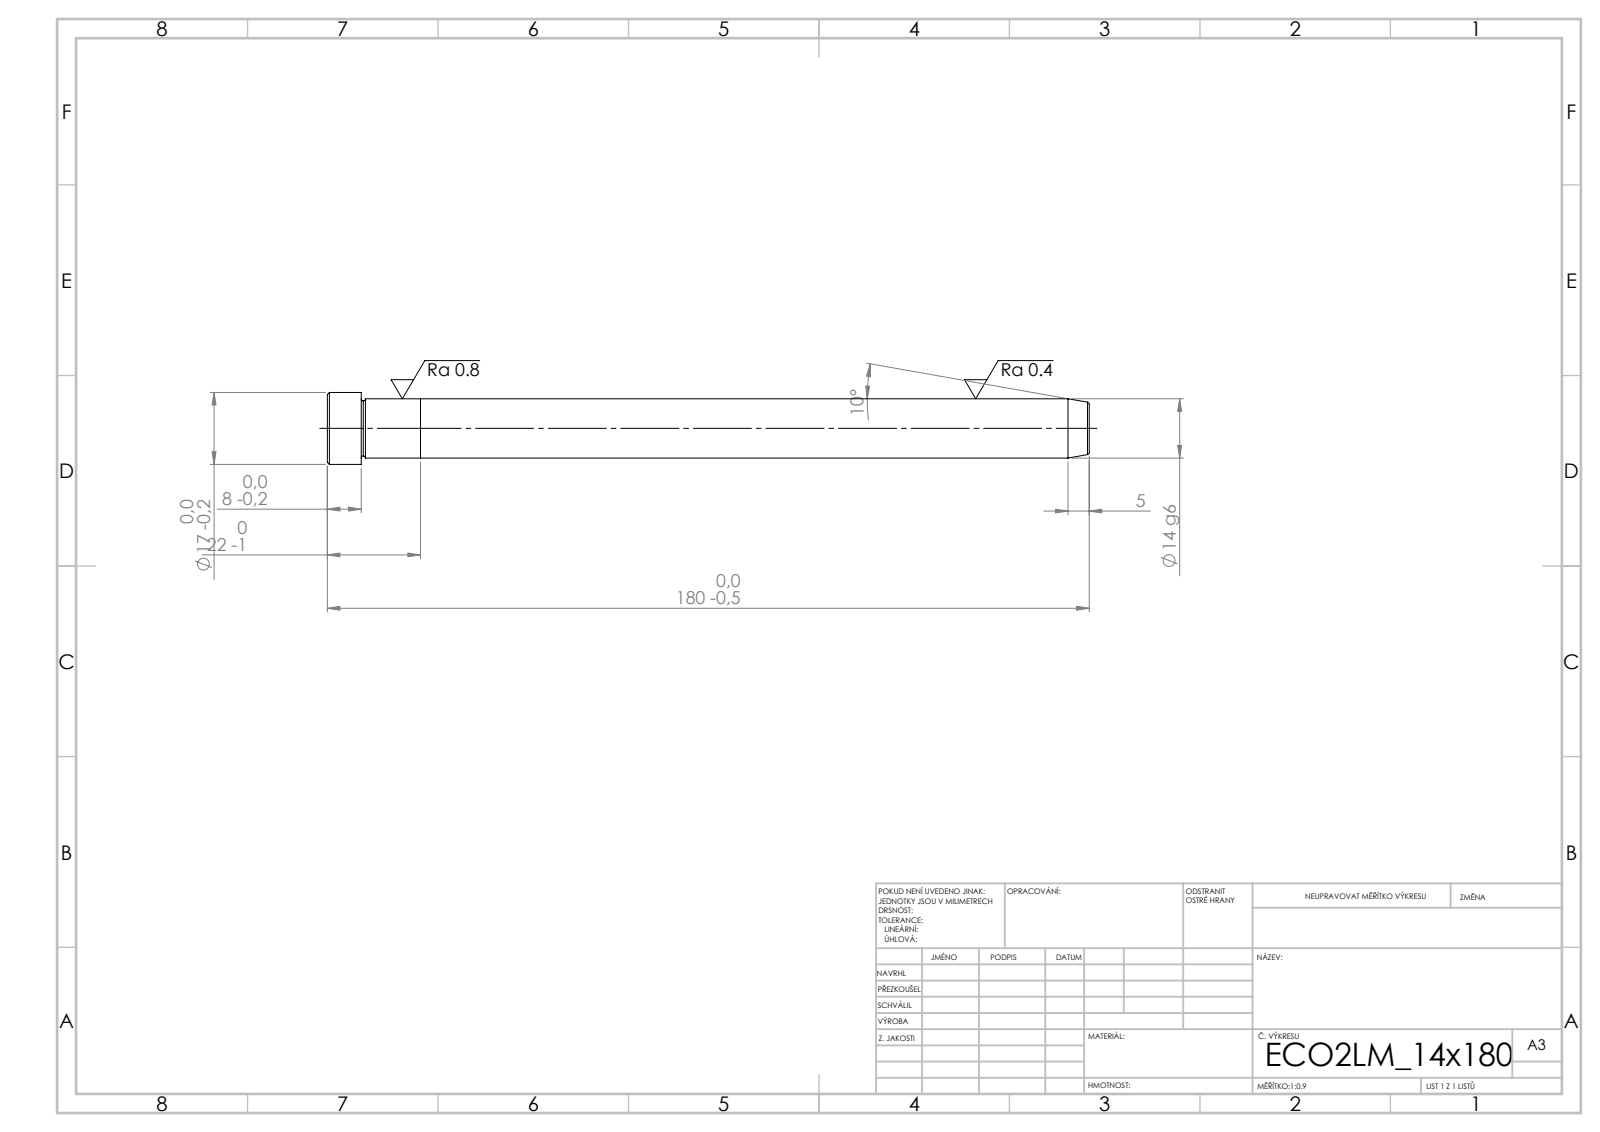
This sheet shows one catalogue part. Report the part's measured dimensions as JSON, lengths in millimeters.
{"step_written_by": "SolidWorks 2019 (CONFIG_CONTROL_DESIGN)", "units": "millimeters", "bodies": {"solids": 2, "faces": 21, "planar": 5, "cylindrical": 6, "other": 10}, "overall_size": [180, 17, 17], "volume_mm3": 28176, "surface_area_mm2": 8708, "round_bosses_or_shafts": [[17, 1], [14, 1]], "face_to_face_distances": [22, 158, 180, 172, 14, 8]}
